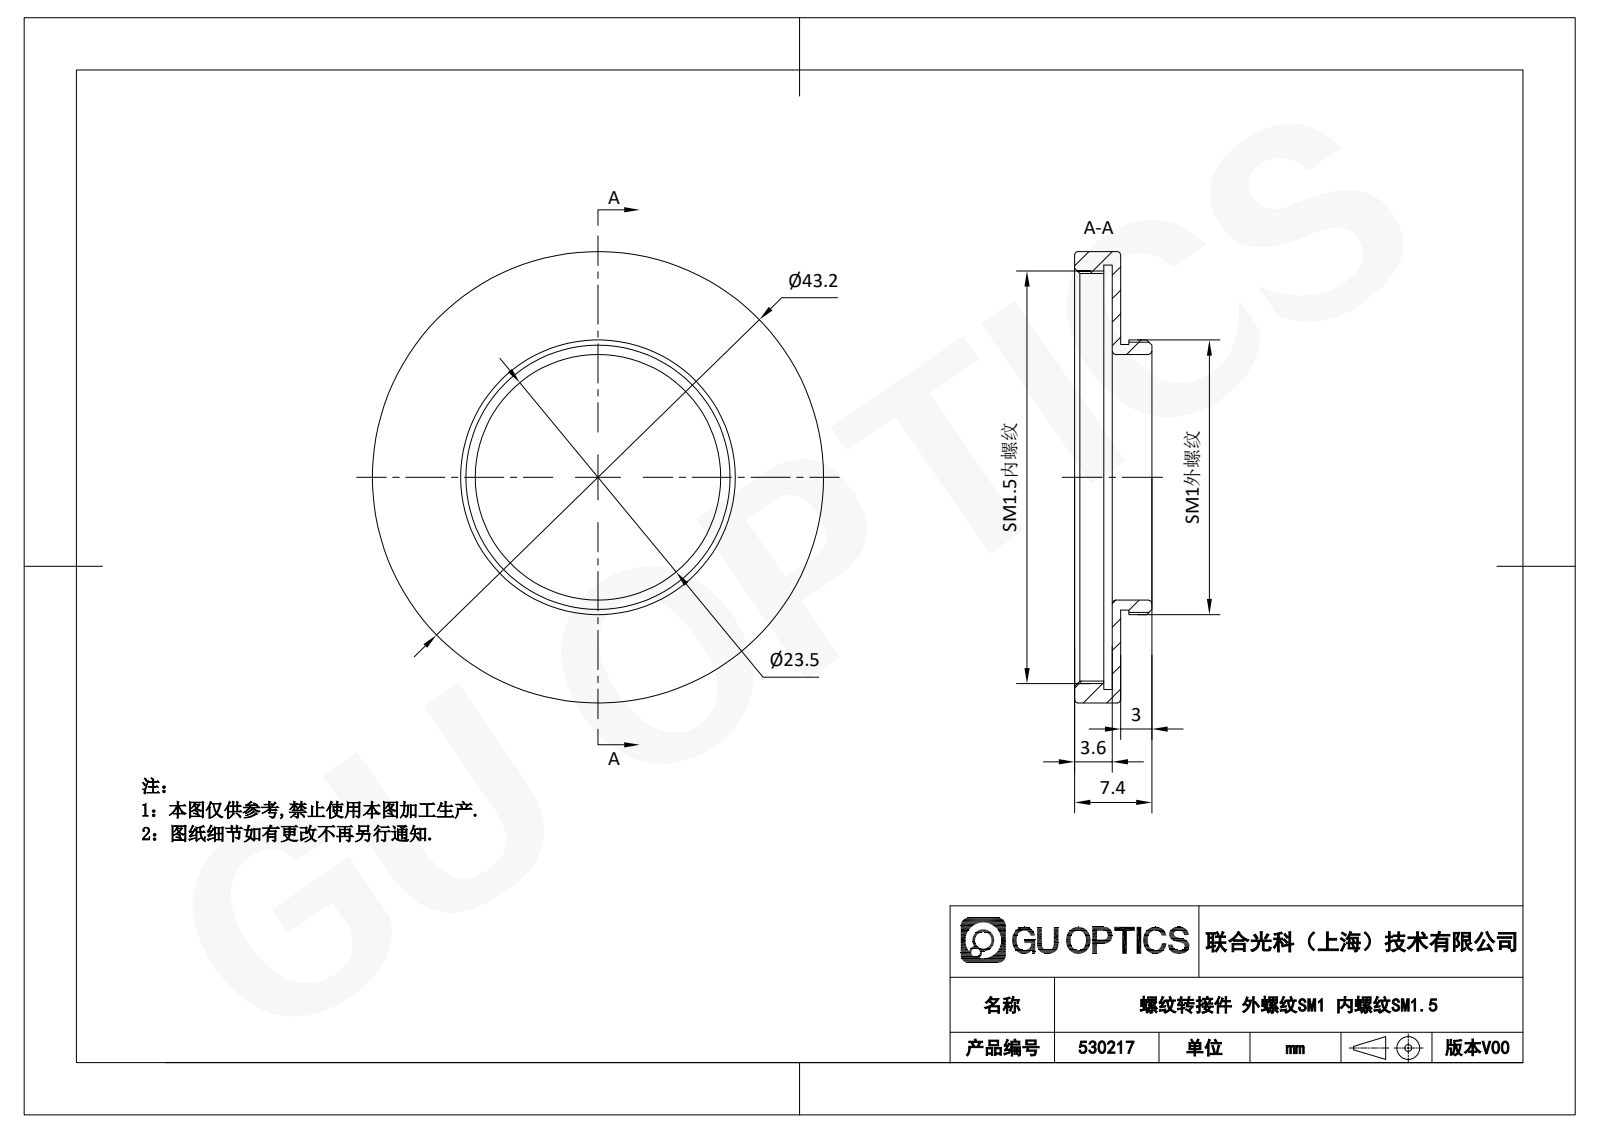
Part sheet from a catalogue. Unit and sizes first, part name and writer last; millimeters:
Units: millimetres
Overall size (bounding box): 43.2 × 43.2 × 7.4
Round holes (diameter × count): ⌀23.5 ×1, ⌀38.99 ×1, ⌀40.59 ×1
Round bosses / shafts (diameter × count): ⌀43.2 ×1, ⌀26.29 ×1, ⌀25.4 ×1
Main face-to-face distances: 0.8, 4.4, 3.6, 1.6, 2.8, 3, 3.8, 4.6, 7.4, 2.2
Volume: 1 989 mm³ · Surface area: 3 790 mm²
Bodies: 1 solid, 18 faces (6 planar, 6 cylindrical, 6 other)
Part name (STEP PRODUCT): 530217
STEP written by: SolidWorks 2020 (CONFIG_CONTROL_DESIGN)
